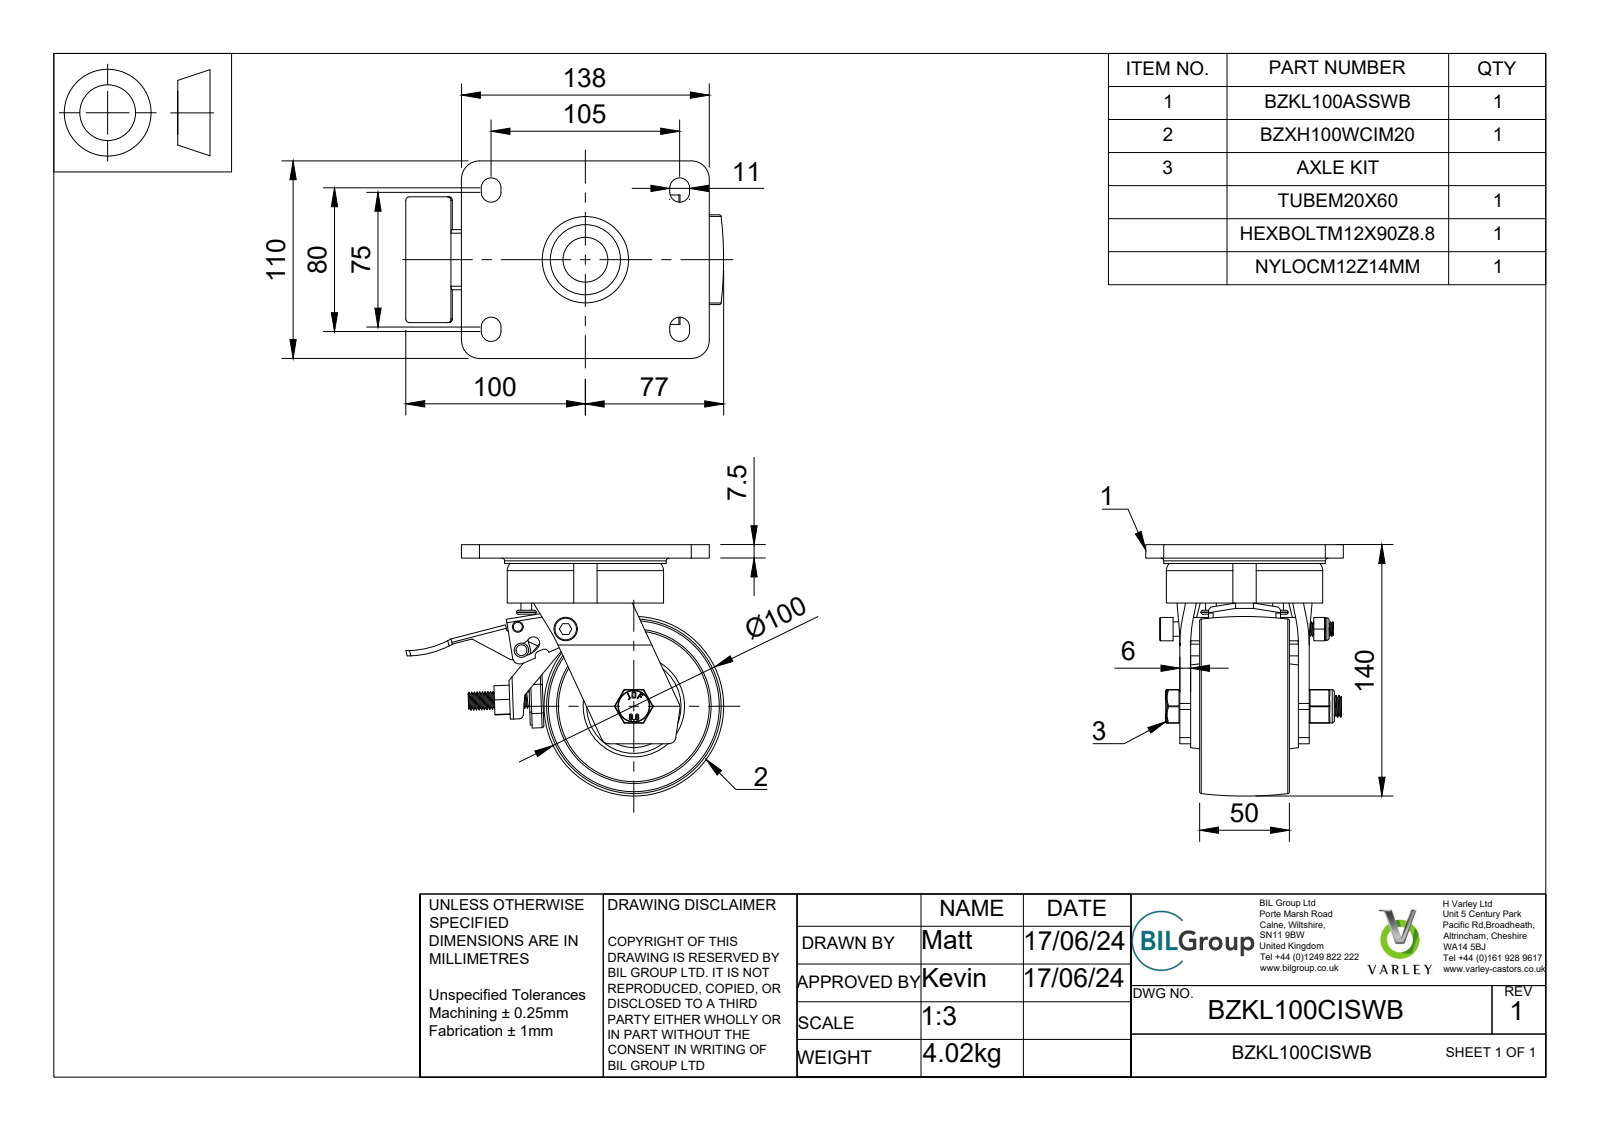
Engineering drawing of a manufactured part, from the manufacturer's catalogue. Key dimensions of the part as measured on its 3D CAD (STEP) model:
Part name (STEP PRODUCT): BZKL100CISWB v3; BZXH100WCIM20 v1; CAST IRON WHEEL; GREASE NIPPLE (+8 more)
STEP written by: Autodesk Translation Framework v13.14.0.145 (AUTOMOTIVE_DESIGN)
Units: millimetres
Bodies: 25 solids, 634 faces (279 planar, 259 cylindrical, 96 other)
Overall size (bounding box): 177 × 140 × 110
Volume: 571 139 mm³ · Surface area: 178 503 mm²
Round holes (diameter × count): ⌀4 ×2, ⌀6 ×2, ⌀8 ×1, ⌀9 ×1, ⌀10 ×1, ⌀12 ×1, ⌀12.5 ×1, ⌀12.75 ×1, ⌀14 ×1, ⌀20.2 ×1, ⌀40.2 ×1, ⌀48 ×1
Round bosses / shafts (diameter × count): ⌀6 ×4, ⌀11 ×2, ⌀8 ×2, ⌀90 ×1, ⌀88 ×1, ⌀19.9 ×1, ⌀18.5 ×1, ⌀17.75 ×1
Partial cylindrical surfaces — rounded edges, fillets, slot ends (radius × count): R0.5 ×26, R1 ×10, R2 ×9, R5.5 ×8, R0.25 ×6, R0.47 ×4, R0.9 ×4, R4 ×4
Main face-to-face distances: 7.5, 6, 25, 34, 26, 1, 40, 33, 32, 66
Hole centre spacings: 10.99, 13.15, 21.28, 21.95, 26.68, 27.32, 57.38, 59.02
